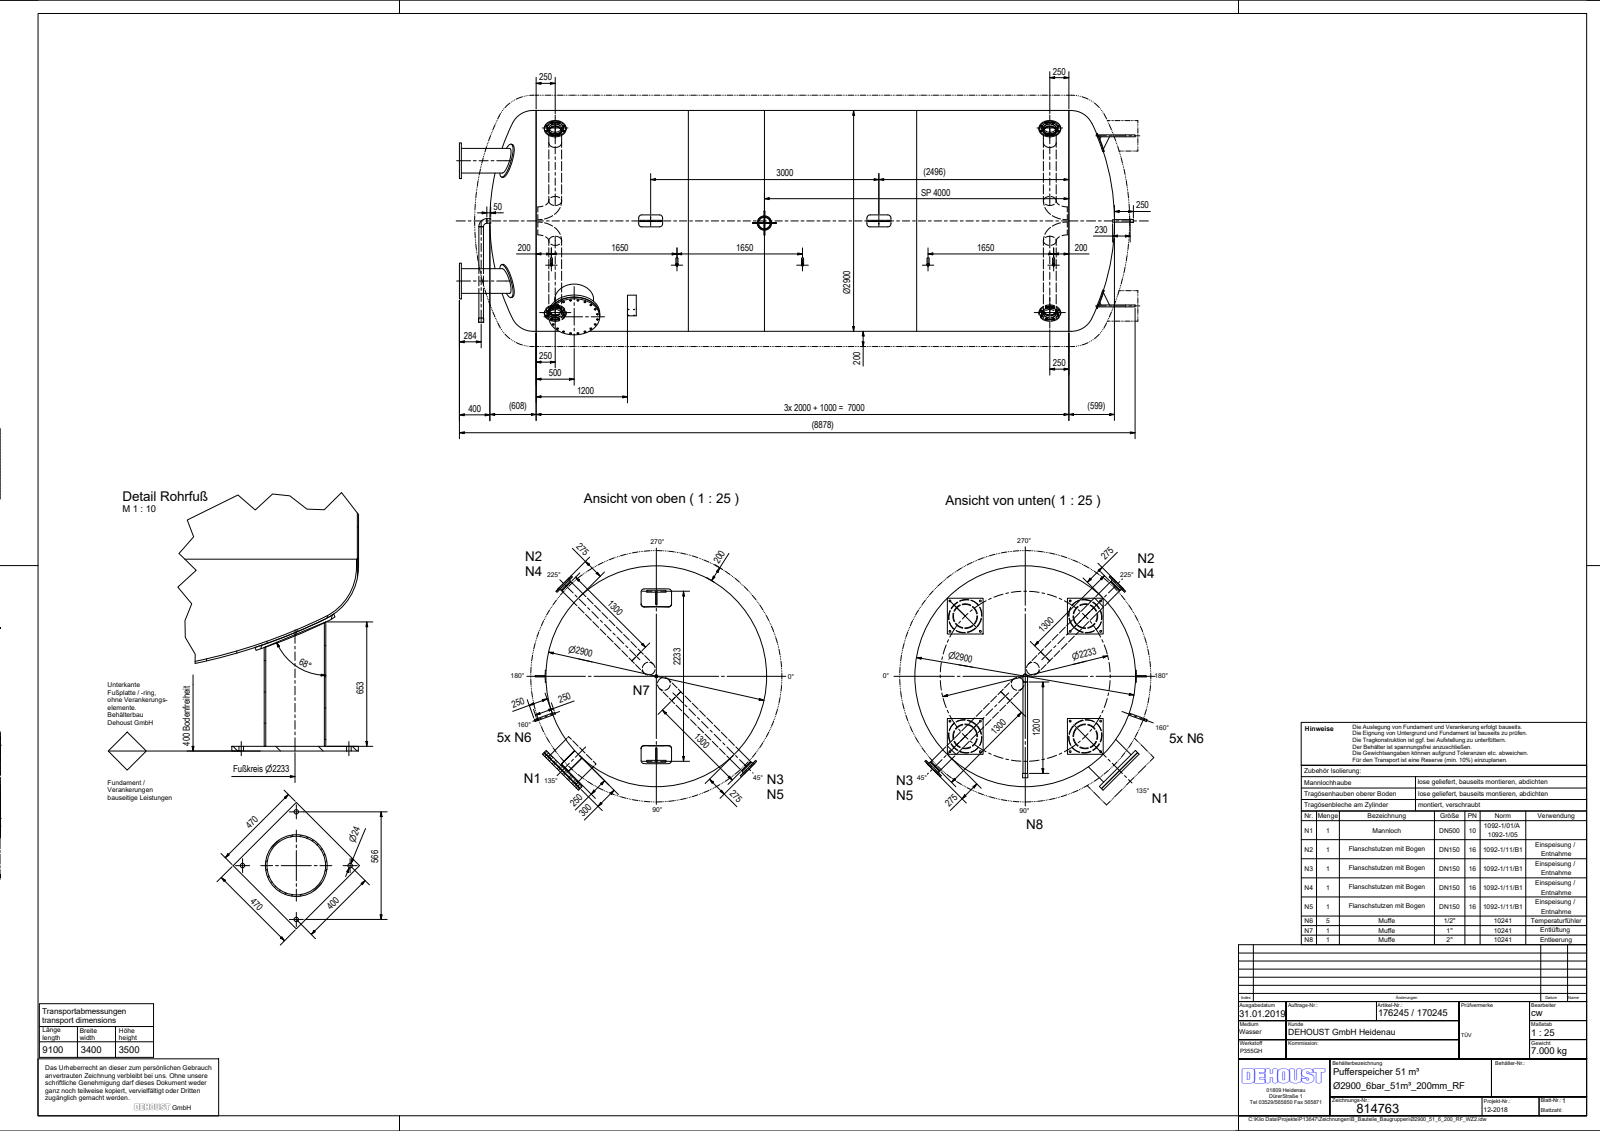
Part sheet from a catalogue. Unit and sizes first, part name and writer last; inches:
Units: inches
Overall size (bounding box): 349.532 × 120.157 × 115.994
Round holes (diameter × count): ⌀1.024 ×36, ⌀0.866 ×32, ⌀0.945 ×16, ⌀6.272 ×8, ⌀0.733 ×5, ⌀0.854 ×5, ⌀1.059 ×5, ⌀0.228 ×4, ⌀6.626 ×4, ⌀12.122 ×4, ⌀0.197 ×2, ⌀2.059 ×2
Round bosses / shafts (diameter × count): ⌀6.626 ×8, ⌀1.059 ×5, ⌀1.039 ×5, ⌀17.717 ×4, ⌀12.752 ×4, ⌀11.22 ×4, ⌀8.346 ×4, ⌀114.173 ×1
Partial cylindrical surfaces — rounded edges, fillets, slot ends (radius × count): R1.654 ×16, R0.394 ×6, R0.236 ×4, R0.197 ×2, R1.417 ×2, R2.835 ×2, R4.921 ×1, R57.48 ×1
Main face-to-face distances: 0.984, 23.622, 19.685, 167.636, 187.321, 166.652, 186.337, 1.102, 127.953, 147.638
Hole centre spacings: 4.724, 12.205, 7.543, 64.961, 19.748, 255.906, 6.681, 17.26
Volume: 50 190 in³ · Surface area: 284 600 in²
Bodies: 58 solids, 449 faces (178 planar, 225 cylindrical, 46 other)
Part name (STEP PRODUCT): Ø2900_51_6_200_RF_WZ2; Klöpper_Gew_Ø2900_8,3; Klöpper_Gew_Ø2900_10,3; Zyl_Ø2900_6x7000_2019 (+8 more)
STEP written by: Autodesk Inventor 2019 (AUTOMOTIVE_DESIGN)
